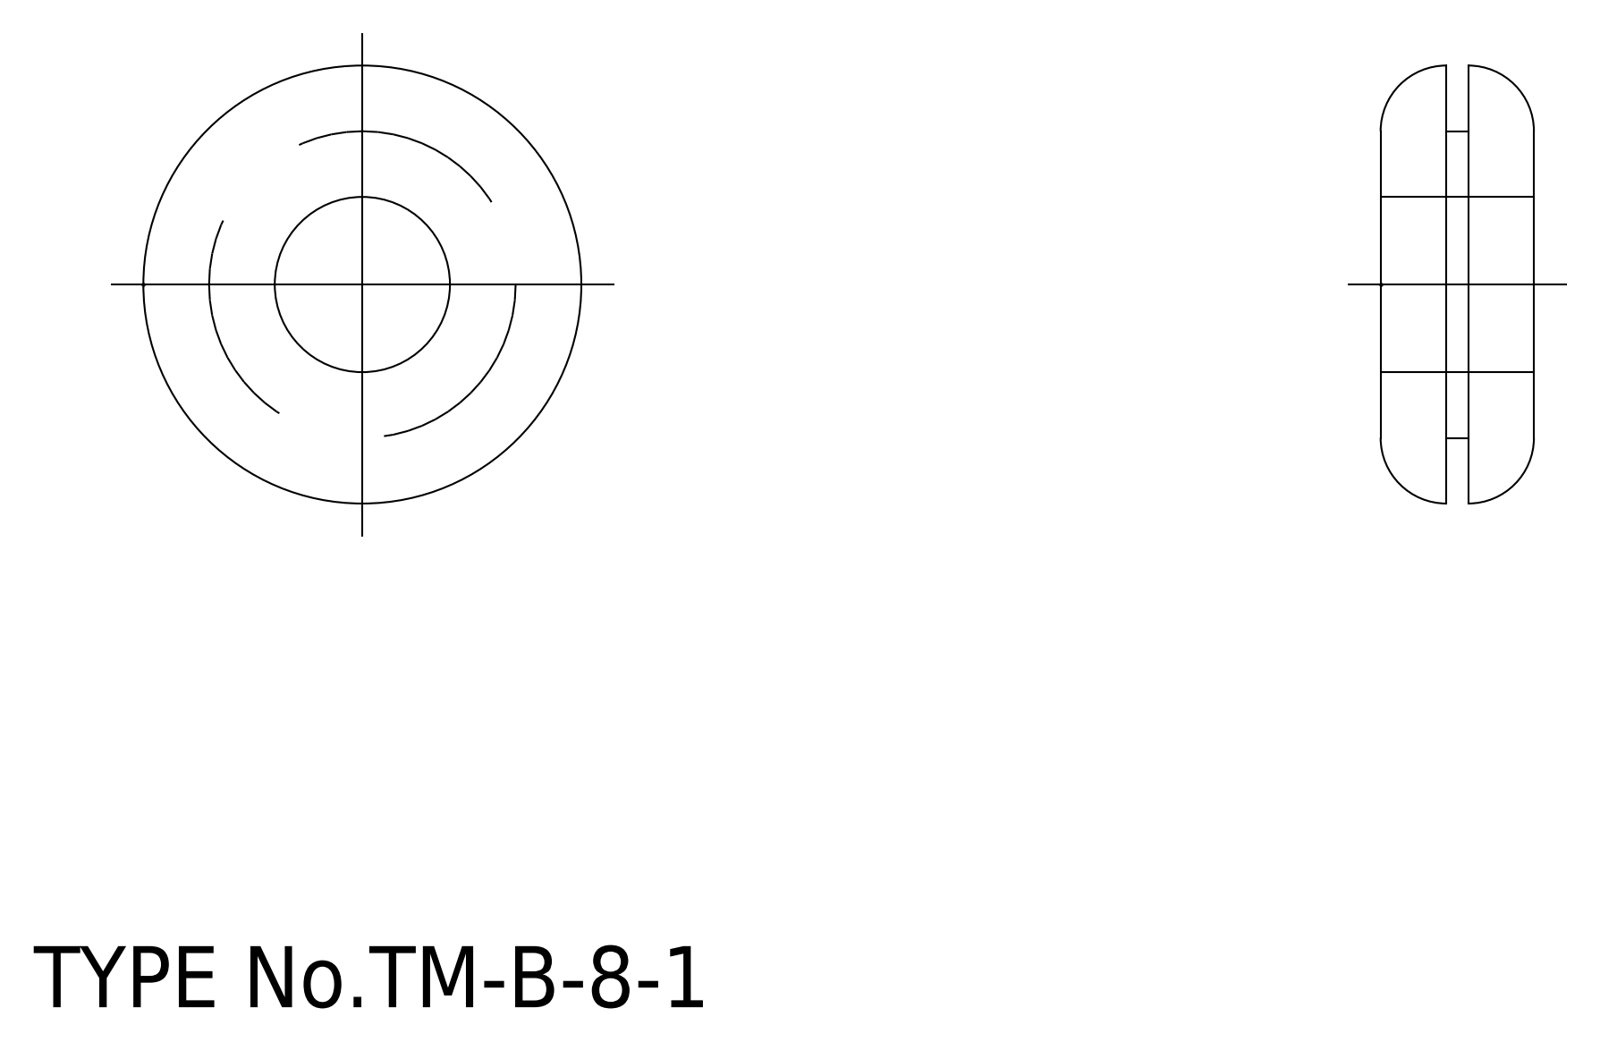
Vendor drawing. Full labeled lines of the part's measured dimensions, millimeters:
Part name (STEP PRODUCT): grommet
STEP written by: CADfix (AUTOMOTIVE_DESIGN)
Units: millimetres
Bodies: 1 solid, 12 faces (0 planar, 0 cylindrical, 12 other)
Overall size (bounding box): 20 × 20 × 7
Volume: 1 464 mm³ · Surface area: 1 276 mm²
